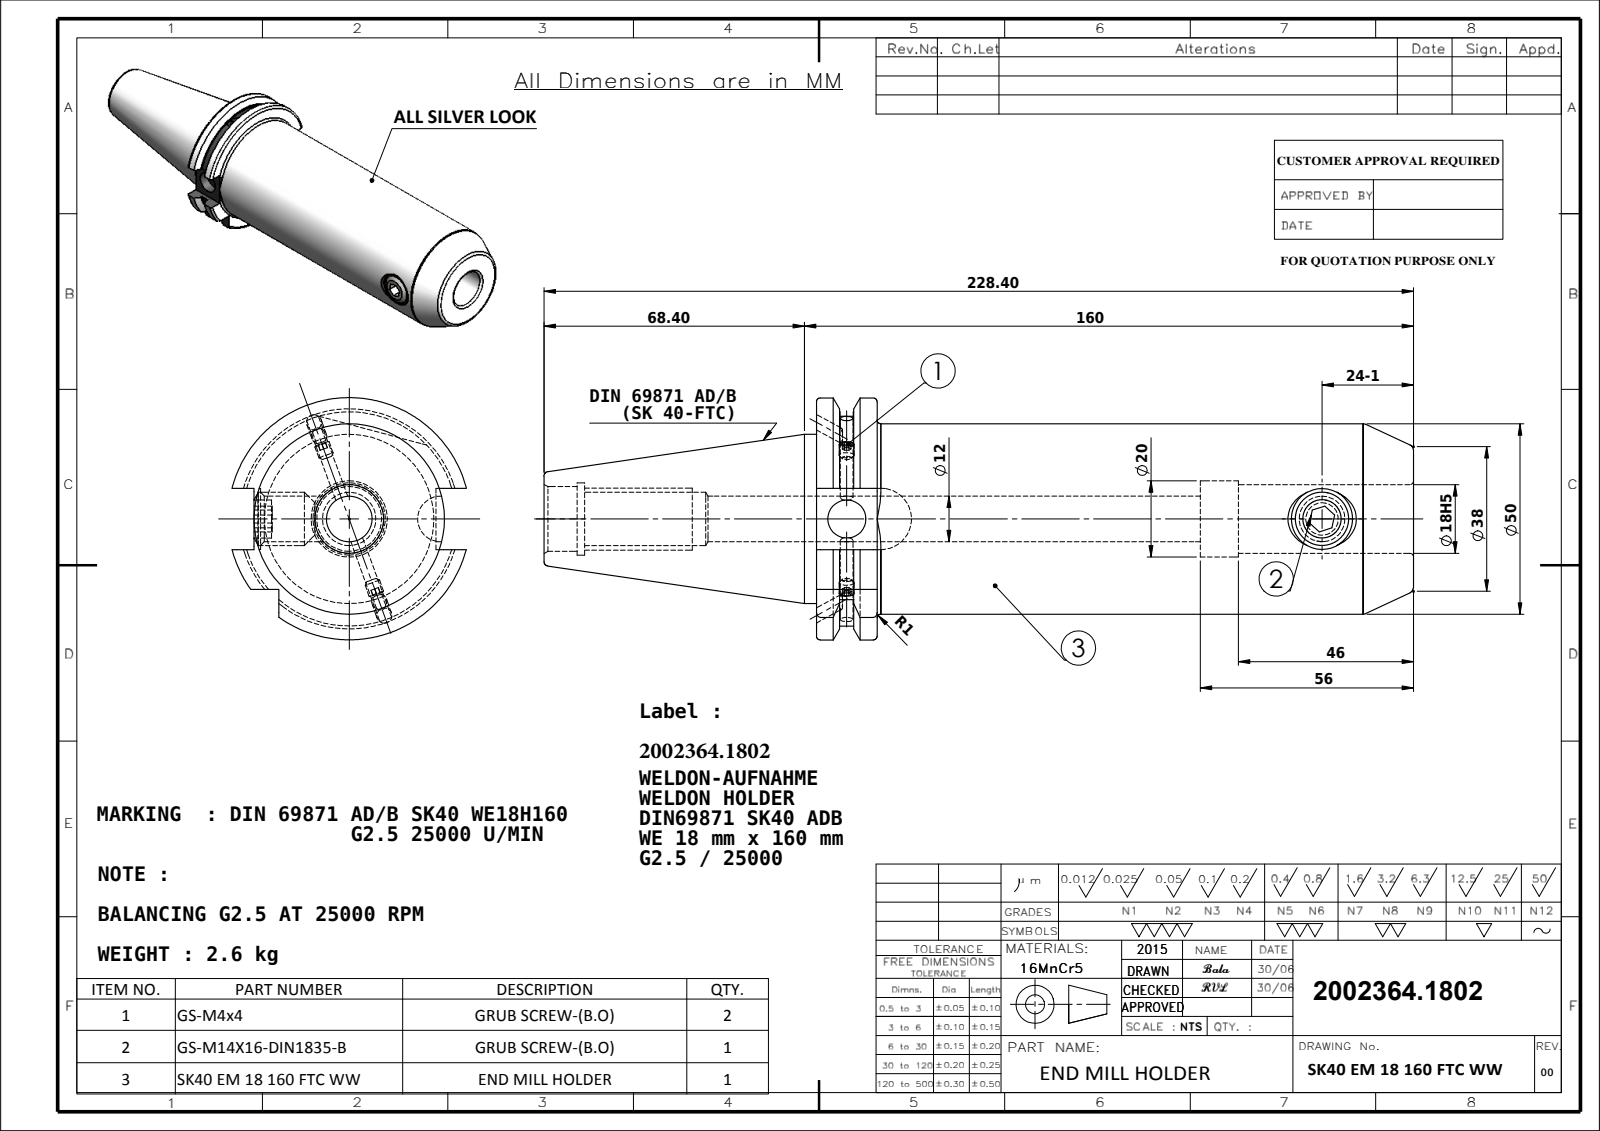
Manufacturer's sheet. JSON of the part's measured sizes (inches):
{"part_name": "91406-WE718160; SK40 EM 18 160 FTC WW; M14X16_ISO 4026 - M12 x 12-N; Copy of M4X4_DIN 913 - M4 x 4-N", "step_written_by": "SolidWorks 2009 (CONFIG_CONTROL_DESIGN)", "units": "inches", "bodies": {"solids": 4, "faces": 163, "planar": 59, "cylindrical": 45, "other": 59}, "overall_size": [8.992, 2.502, 2.42], "volume_in3": 21.13, "surface_area_in2": 78.23, "round_holes": [[0.472, 2], [0.13, 1], [0.394, 1], [0.551, 1], [0.63, 1], [0.669, 1], [0.709, 1], [0.748, 1], [0.787, 1]], "round_bosses_or_shafts": [[0.157, 2], [1.969, 1], [1.75, 1], [0.551, 1]], "partial_cylinders_radius": [[0.317, 1], [1.107, 1], [1.251, 1]], "face_to_face_distances": [6.173, 0.626, 5.547, 1.882, 3.969, 3.343, 2.205, 0.634, 2.819, 3.445], "hole_center_spacings": [4.915]}
